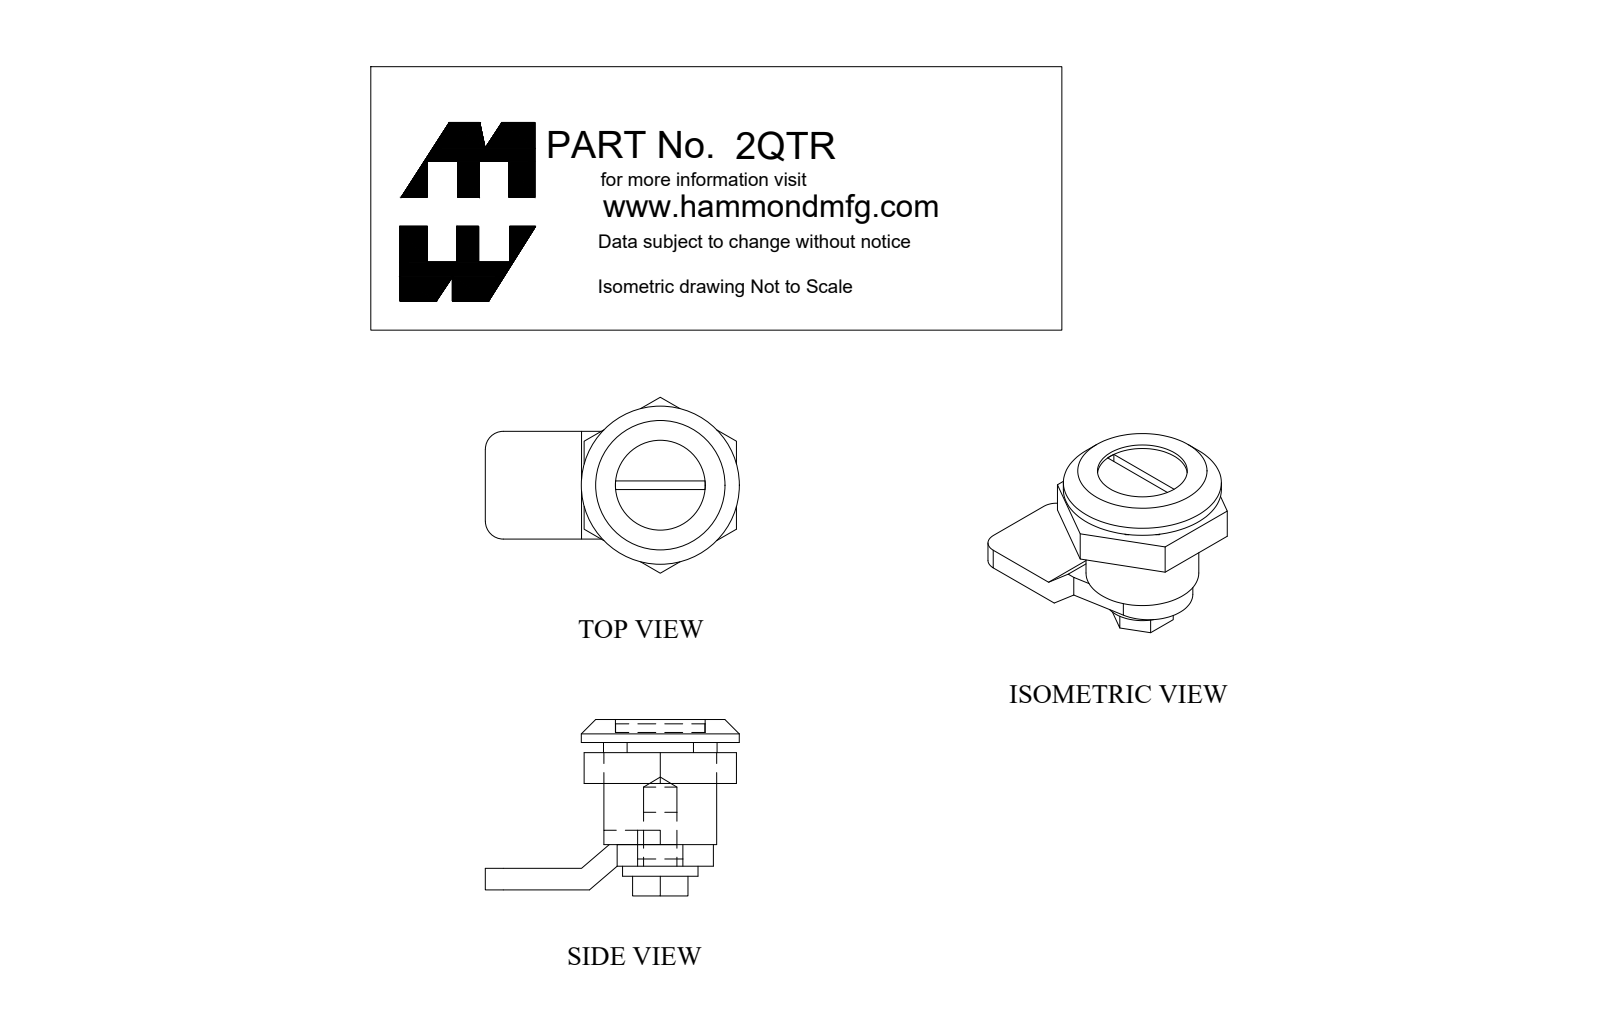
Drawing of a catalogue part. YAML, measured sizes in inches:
part_name: "2QTR"
step_written_by: "SolidWorks 2018 (AUTOMOTIVE_DESIGN)"
units: inches
bodies: {solids: 4, faces: 71, planar: 57, cylindrical: 12, other: 2}
overall_size: [1.768, 1.227, 1.224]
volume: 0.76
surface_area: 10.85
round_holes:
  - {diameter: 0.232, count: 1}
  - {diameter: 0.625, count: 1}
  - {diameter: 0.785, count: 1}
round_bosses_or_shafts:
  - {diameter: 1.1, count: 1}
  - {diameter: 0.525, count: 1}
partial_cylinders:
  - {radius: 0.125, count: 2}
  - {radius: 0.307, count: 1}
  - {radius: 0.312, count: 1}
face_to_face_distances: [0.15, 0.64, 0.315, 0.955, 0.07, 0.15, 0.165, 0.805, 0.74, 0.59]
